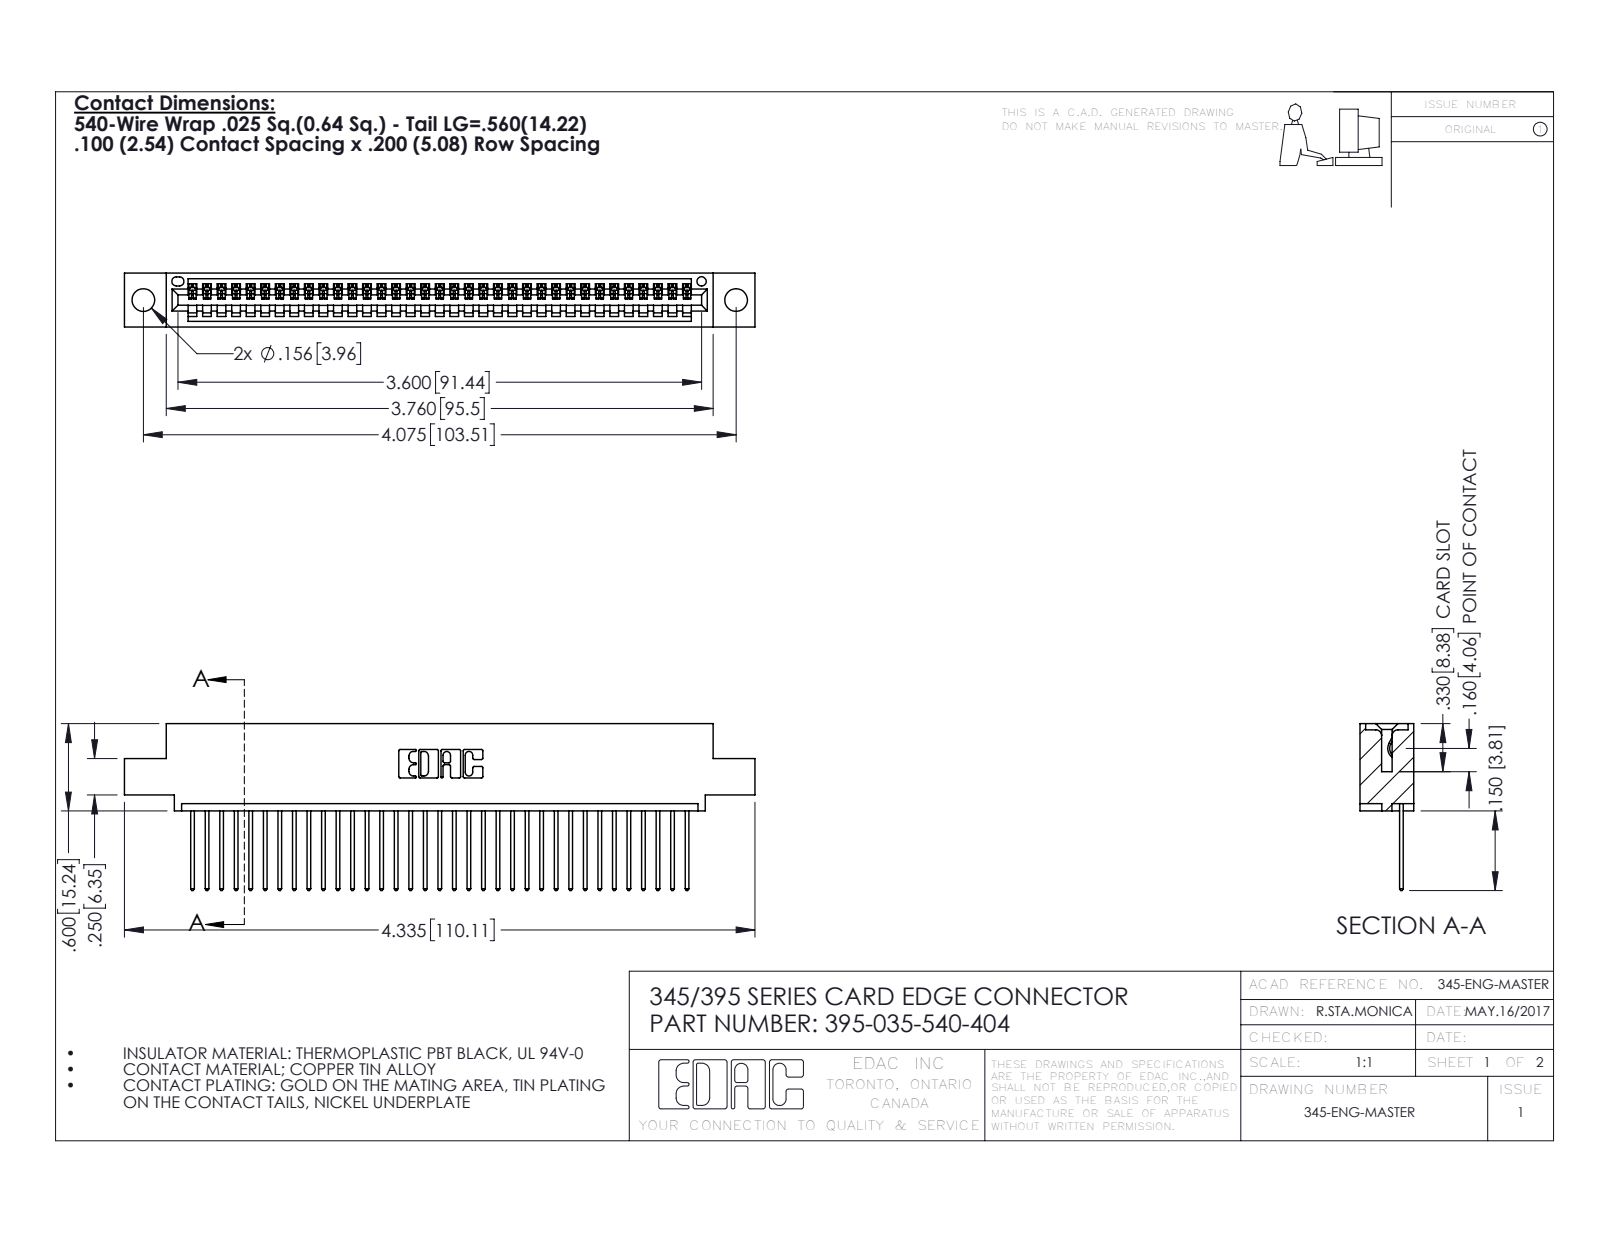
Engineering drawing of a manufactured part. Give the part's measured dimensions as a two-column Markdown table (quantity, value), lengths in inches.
| quantity | value |
| --- | --- |
| part name | 395-035-540-404; 345 Part_0.110 Offset - 0.156 Dia-TH; 345-292-001_345-293-140 |
| STEP written by | SolidWorks 2016 (CONFIG_CONTROL_DESIGN) |
| units | inches |
| bodies | 36 solids, 2160 faces (1484 planar, 676 cylindrical, 0 other) |
| overall size | 4.335 × 1.147 × 0.37 |
| volume | 0.628 in³ |
| surface area | 21.4 in² |
| round holes (diameter × count) | 0.156 × 2, 0.064 × 1 |
| partial cylindrical surfaces (radius × count) | 0.006 × 70, 0.01 × 70, 0.01 × 22, 0.007 × 6, 0.031 × 6, 0.026 × 3, 0.031 × 2, 0.04 × 2 |
| main face-to-face distances | 0.298, 0.072, 0.37, 0.098, 0.272, 0.025, 0.2, 0.225, 0.149, 0.072 |
| hole center spacings | 0.27, 3.839, 4.075 |
